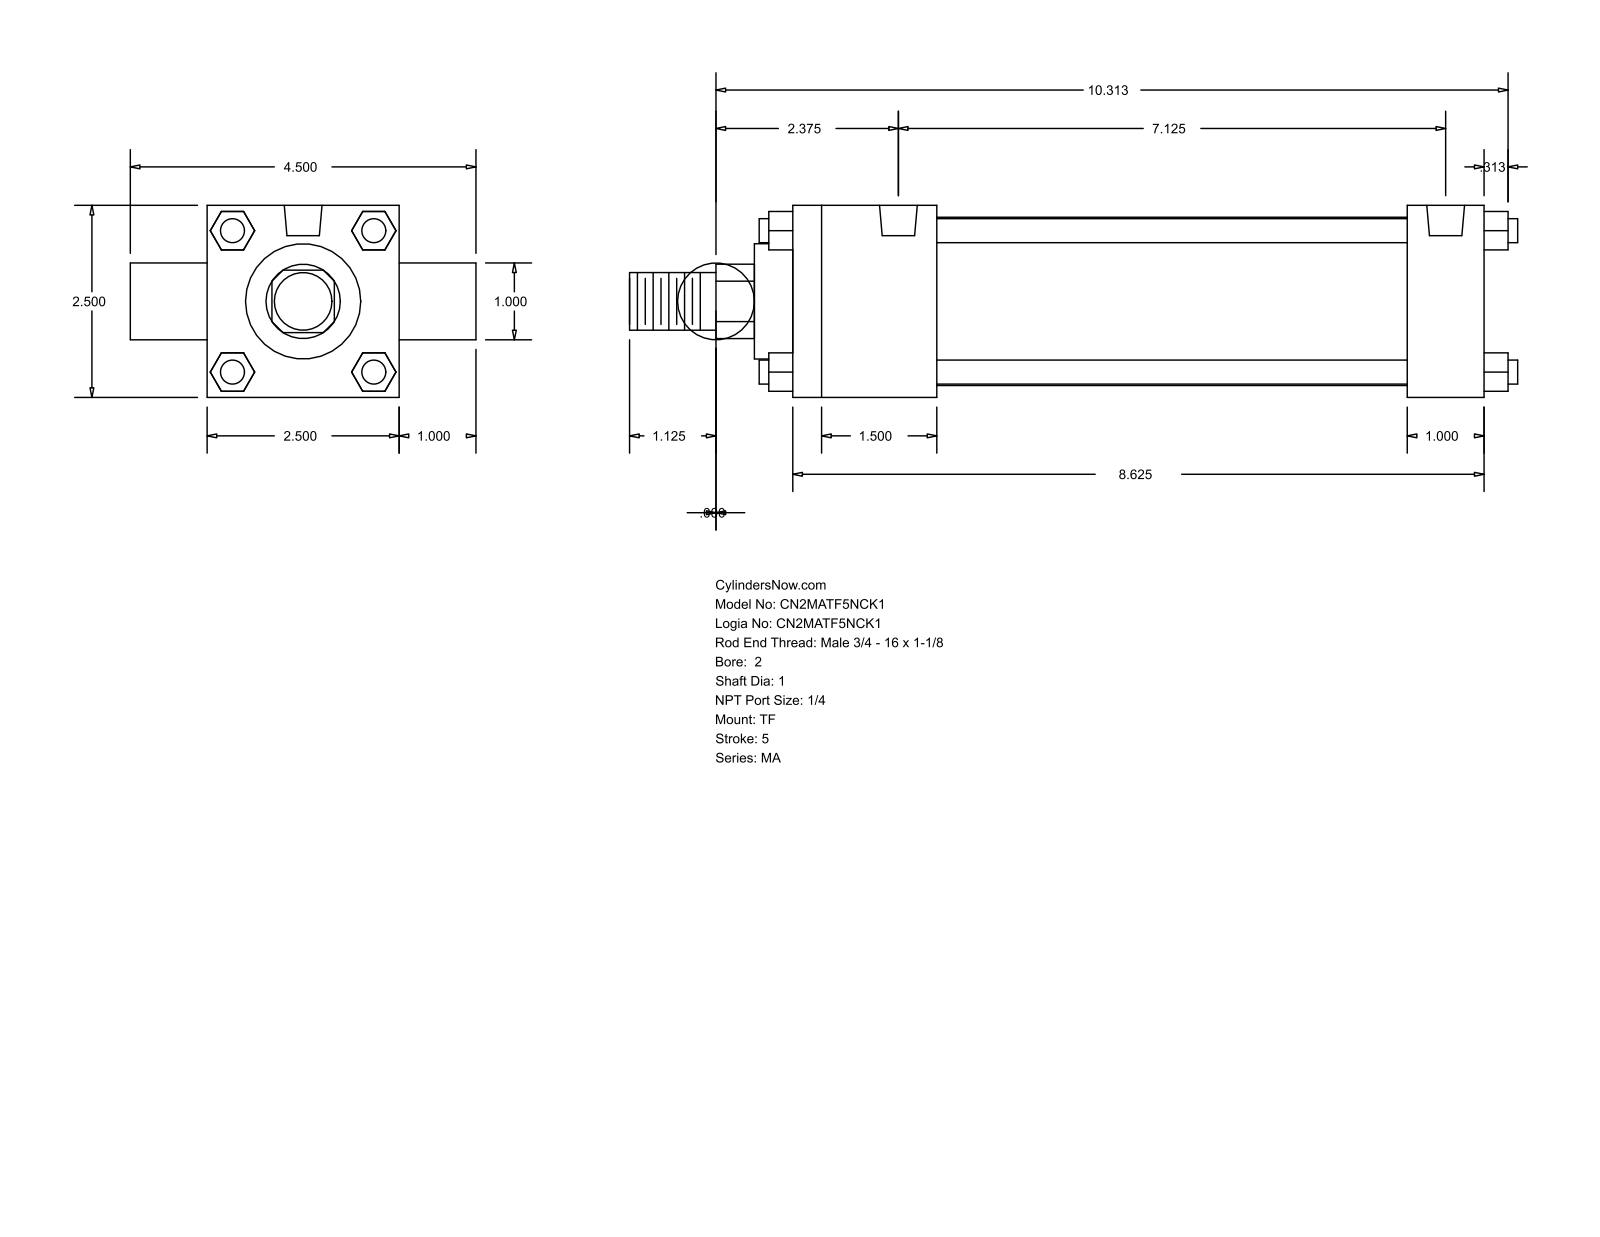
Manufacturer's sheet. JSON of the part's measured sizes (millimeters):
{"part_name": "MA_TF__0200_1", "step_written_by": "GSSL Pune (CONFIG_CONTROL_DESIGN)", "units": "millimeters", "bodies": {"solids": 0, "faces": 120, "planar": 92, "cylindrical": 28, "other": 0}, "overall_size": [293.69, 114.3, 63.5], "round_holes": [[7.94, 3], [12.49, 2]], "round_bosses_or_shafts": [[7.94, 4], [25.4, 2], [55.63, 1], [38.1, 1], [19.05, 1]], "partial_cylinders_radius": [[12.29, 1]], "face_to_face_distances": [63.5, 25.4, 228.6, 12.7, 47.63, 203.2, 155.57, 180.97, 88.9, 23.37], "hole_center_spacings": [180.97]}
